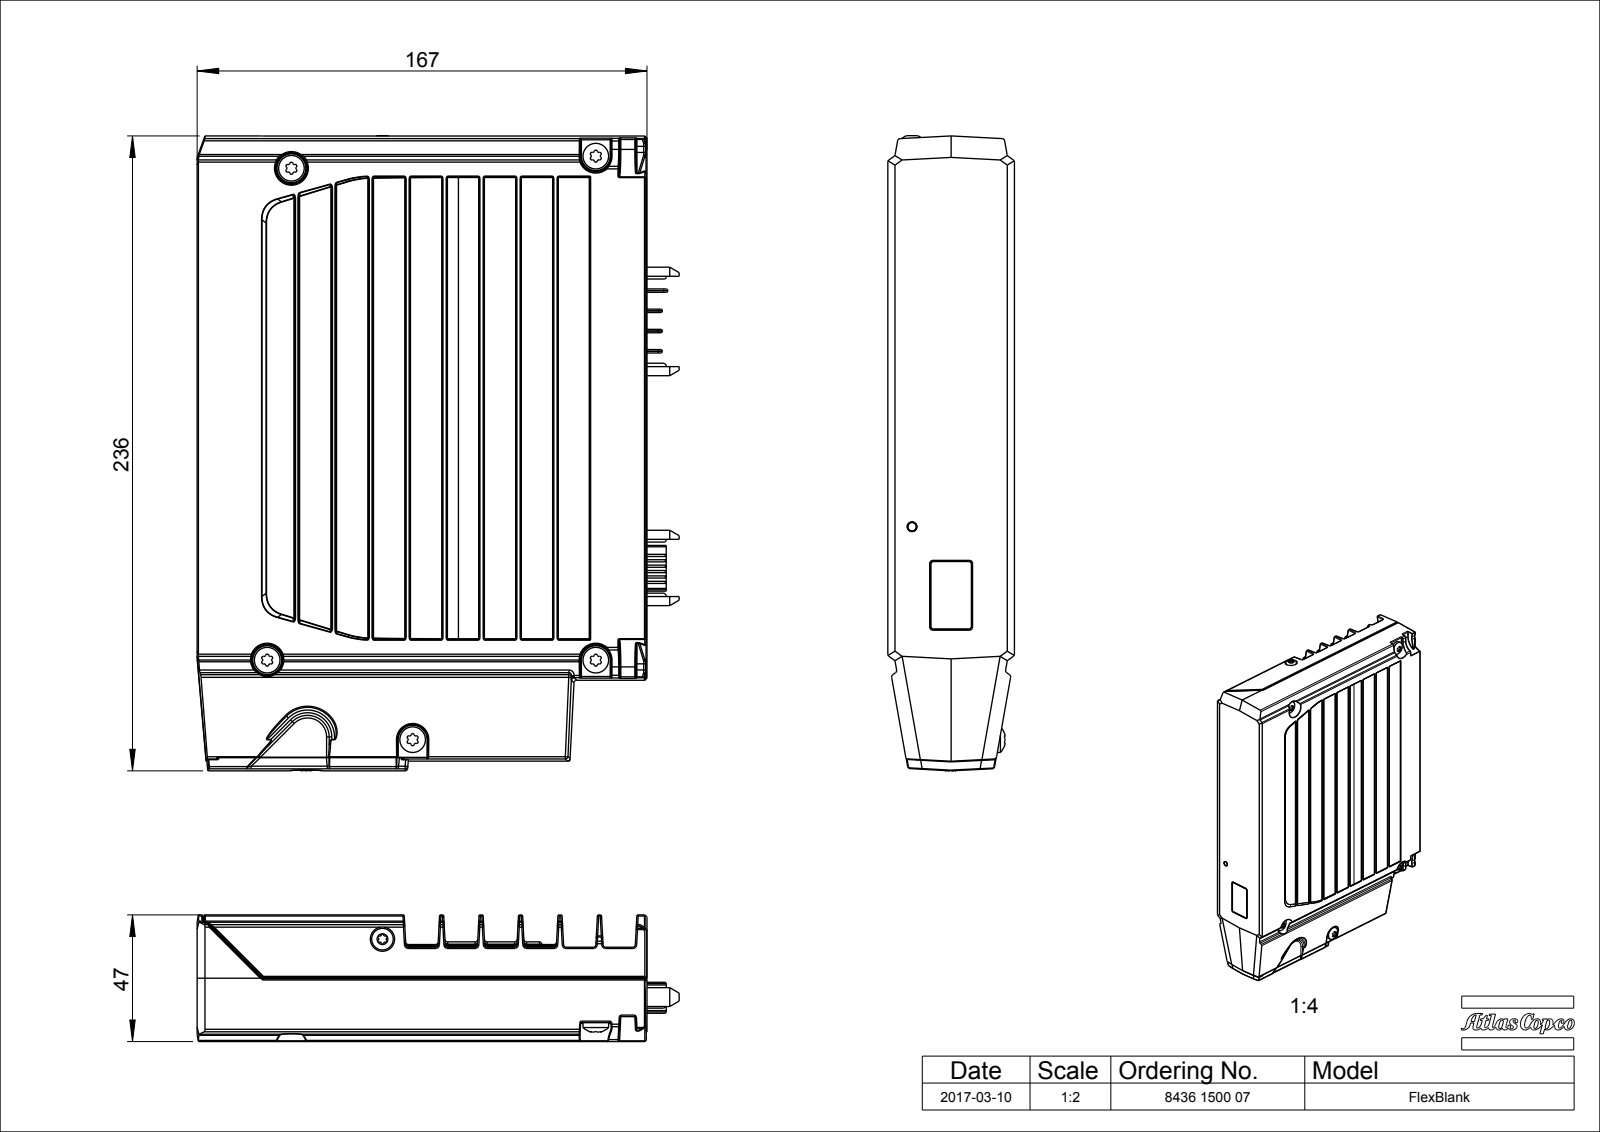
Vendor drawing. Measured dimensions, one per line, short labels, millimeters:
name: 4222204510; FD_POWER-PLUG_35; FD_SIGNAL-PLUG_35; 4222195880_DESIGN_ASM (+7 more)
written by: CREO PARAMETRIC BY PTC INC, 2020281 (CONFIG_CONTROL_DESIGN)
unit: mm
bodies: 16 solids, 11286 faces (3738 planar, 3674 cylindrical, 3874 other)
size: 235.1 × 178.95 × 47
volume: 834 085 mm³; area: 590 105 mm²
holes: 1× ⌀2.7, 1× ⌀3, 1× ⌀3.3, 1× ⌀4.5, 1× ⌀9
bosses: 39× ⌀1, 6× ⌀9.5, 6× ⌀5, 2× ⌀4, 1× ⌀8.4, 1× ⌀8
rounds: 581× R1, 361× R0.3, 280× R0.5, 77× R0.1, 72× R0.58, 32× R0.1, 16× R1.02, 9× R5
face distances: 3, 44, 2, 12, 4.91, 39.09, 14.63, 32, 1, 13.63
hole spacings: 38.07, 43.09
